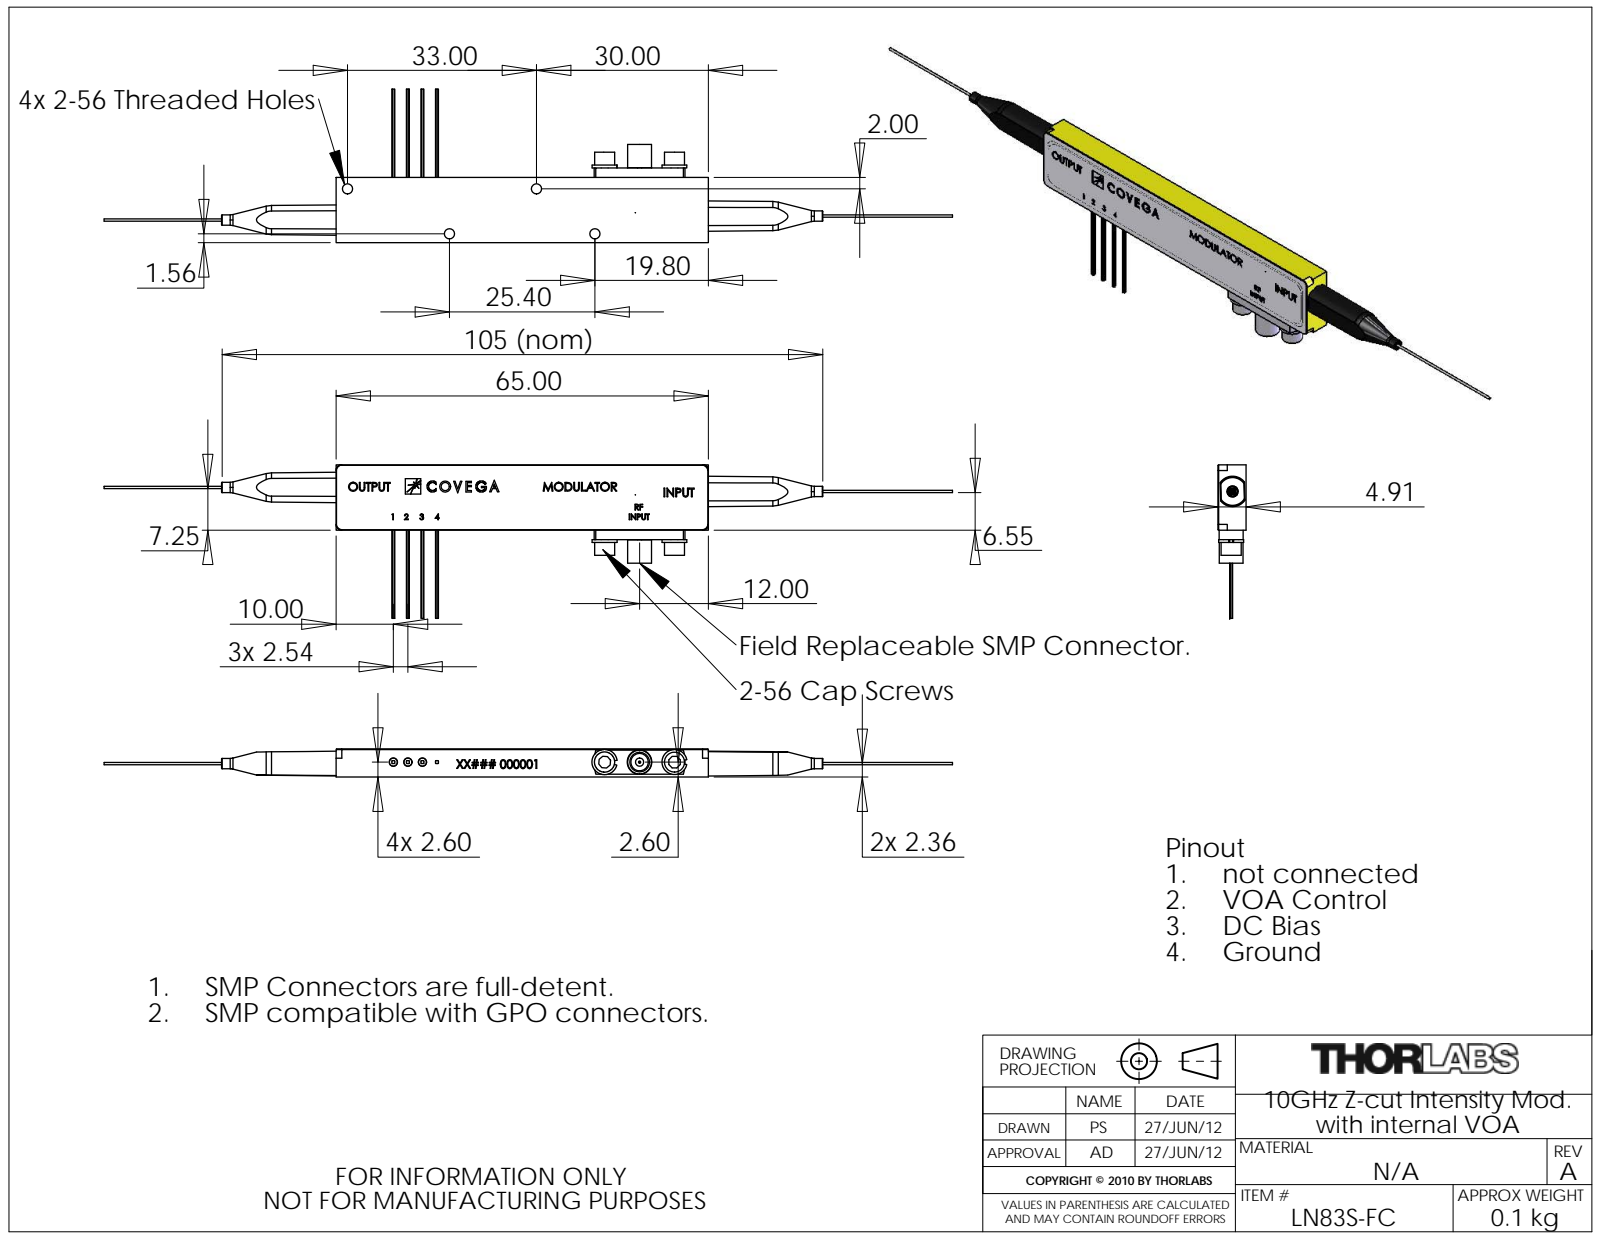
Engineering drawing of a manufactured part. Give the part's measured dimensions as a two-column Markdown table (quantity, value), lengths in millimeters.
| quantity | value |
| --- | --- |
| part name | LN81 |
| STEP written by | SolidWorks 2011 (AUTOMOTIVE_DESIGN) |
| units | millimeters |
| bodies | 0 solids, 423 faces (263 planar, 77 cylindrical, 83 other) |
| overall size | 138.85 × 26.8 × 4.91 |
| round holes (diameter × count) | 1.78 × 4, 0.9 × 2, 1.42 × 1, 1.93 × 1, 3.05 × 1, 3.18 × 1 |
| round bosses / shafts (diameter × count) | 4.37 × 2, 3.5 × 2, 1.8 × 2, 0.4 × 2, 4.16 × 1, 1.45 × 1, 1.42 × 1, 1.4 × 1 |
| partial cylindrical surfaces (radius × count) | 0.1 × 16, 0.9 × 4, 1 × 4, 0.85 × 1, 0.96 × 1, 0.97 × 1, 5.58 × 1, 5.58 × 1 |
| main face-to-face distances | 4.91, 11.4, 4.78, 13.05, 1.65, 0.5, 0.51, 65, 2.54, 4.41 |
| hole center spacings | 0.7, 2.35, 12.86, 16.91, 17.1, 17.95, 19.45, 25.4 |
